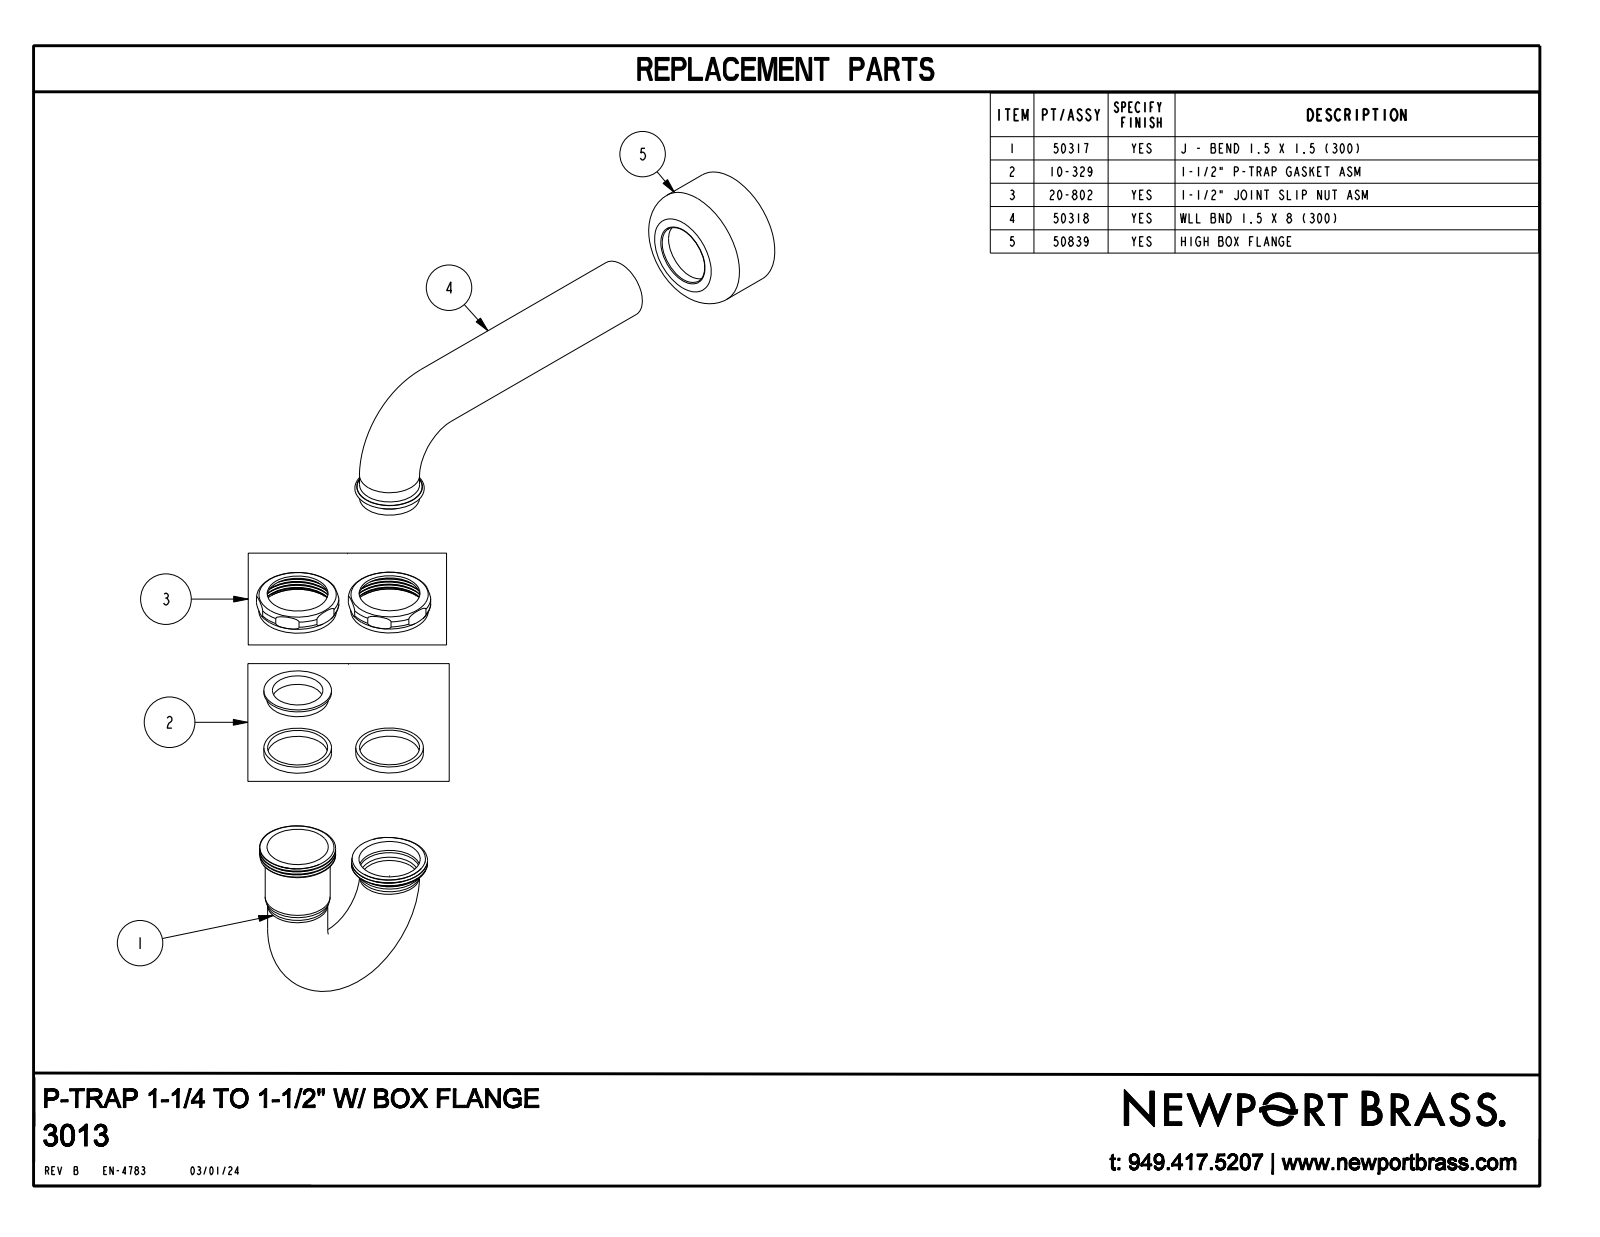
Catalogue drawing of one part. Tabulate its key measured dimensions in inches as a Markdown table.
| quantity | value |
| --- | --- |
| part name | 3013 |
| STEP written by | CREO PARAMETRIC BY PTC INC, 2018500 (CONFIG_CONTROL_DESIGN) |
| units | inches |
| bodies | 3 solids, 237 faces (45 planar, 98 cylindrical, 94 other) |
| overall size | 12.468 × 6.623 × 3 |
| volume | 31.07 in³ |
| surface area | 258.4 in² |
| round holes (diameter × count) | 1.52 × 2, 1.78 × 2, 1.23 × 1, 1.28 × 1, 1.3 × 1, 1.51 × 1, 2.954 × 1 |
| round bosses / shafts (diameter × count) | 1.5 × 3, 1.94 × 2, 1.69 × 2, 1.625 × 2, 3 × 1, 1.715 × 1, 1.556 × 1, 1.406 × 1 |
| partial cylindrical surfaces (radius × count) | 0.939 × 2, 1.03 × 2 |
| main face-to-face distances | 2.815, 1.97, 1.727, 1.75, 0.023, 1.122, 4.784, 0.845, 1.97, 0.75 |
| hole center spacings | 3.25 |
